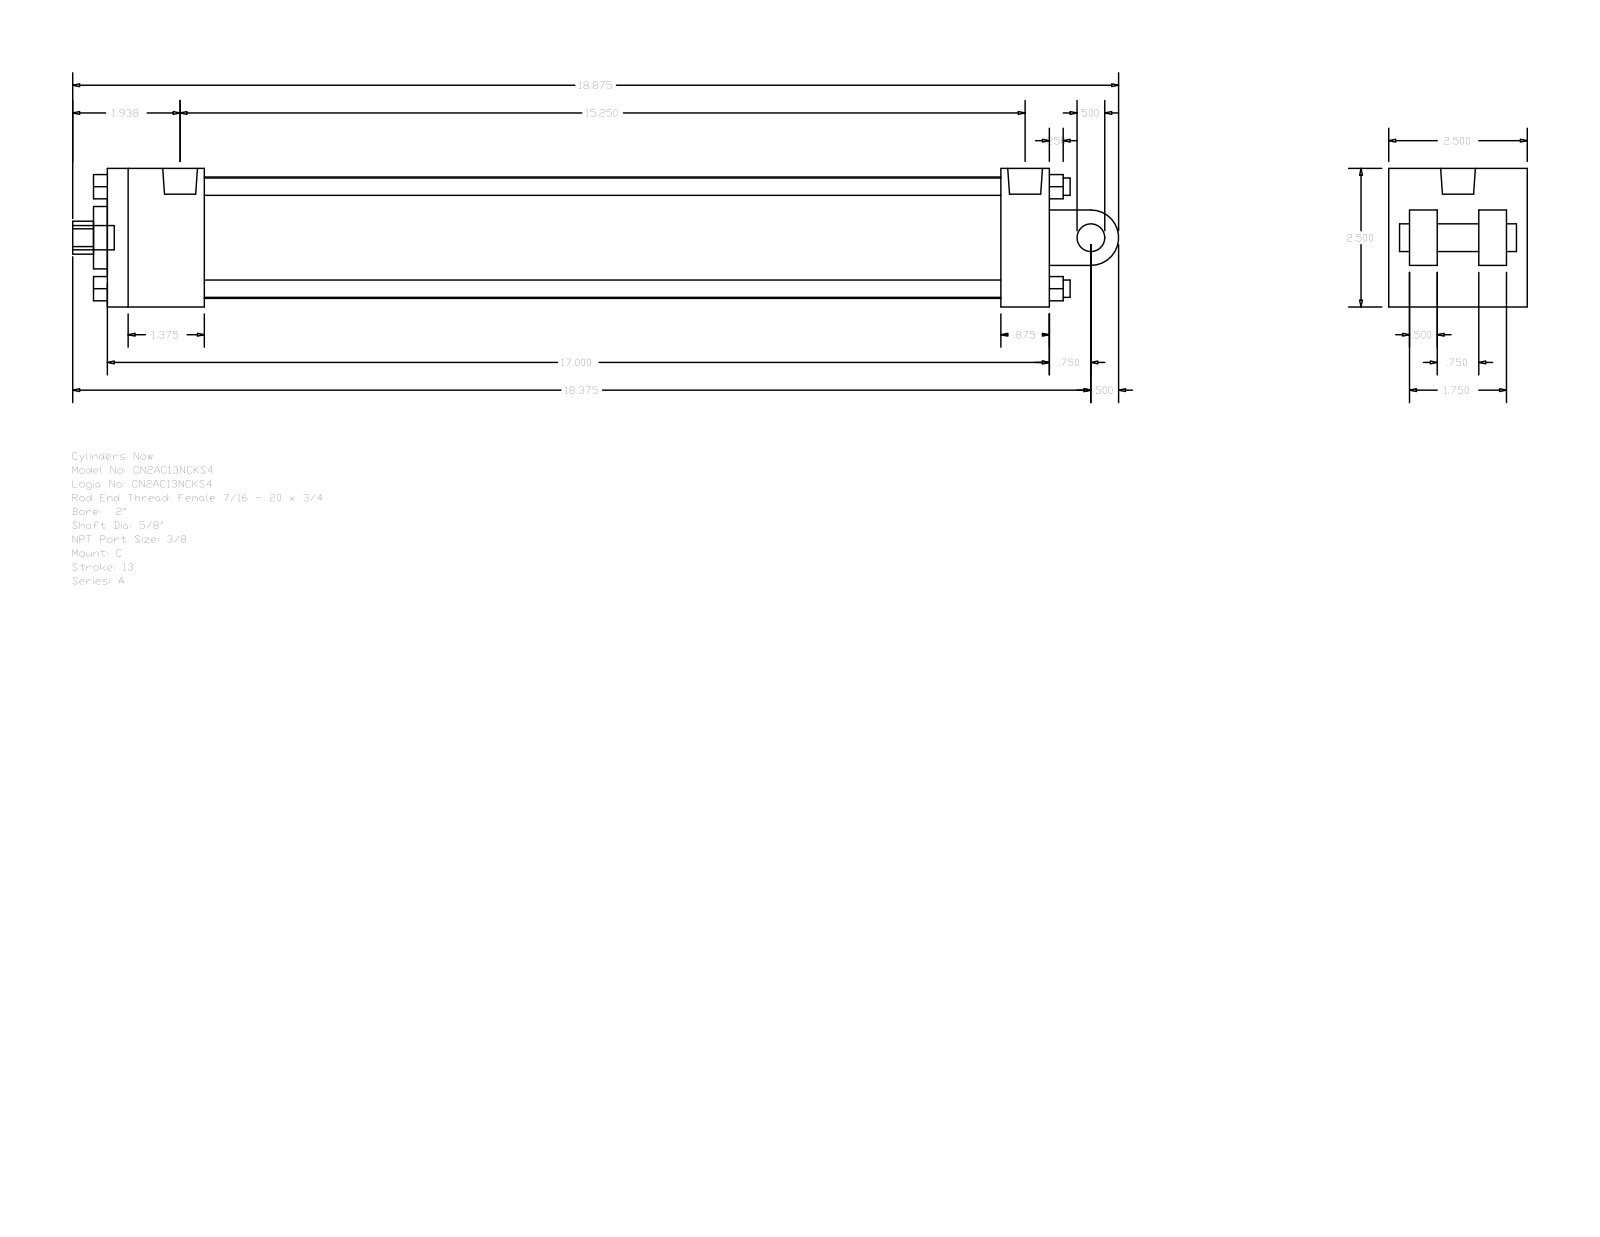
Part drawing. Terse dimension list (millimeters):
name: A_C__0200_0.625
written by: GSSL Pune (CONFIG_CONTROL_DESIGN)
unit: mm
bodies: 0 solids, 135 faces (102 planar, 33 cylindrical, 0 other)
size: 479.43 × 63.5 × 63.5
holes: 2× ⌀5.56, 1× ⌀15.88, 1× ⌀15.93, 1× ⌀28.57, 1× ⌀55.63
bosses: 4× ⌀7.94, 2× ⌀5.56, 1× ⌀15.93, 1× ⌀12.7, 1× ⌀11.11
rounds: 1× R7.54, 1× R12.7
face distances: 63.5, 431.8, 44.45, 9.52, 387.35, 409.57, 365.12, 22.23, 12.7, 41.28
hole spacings: 3.97
